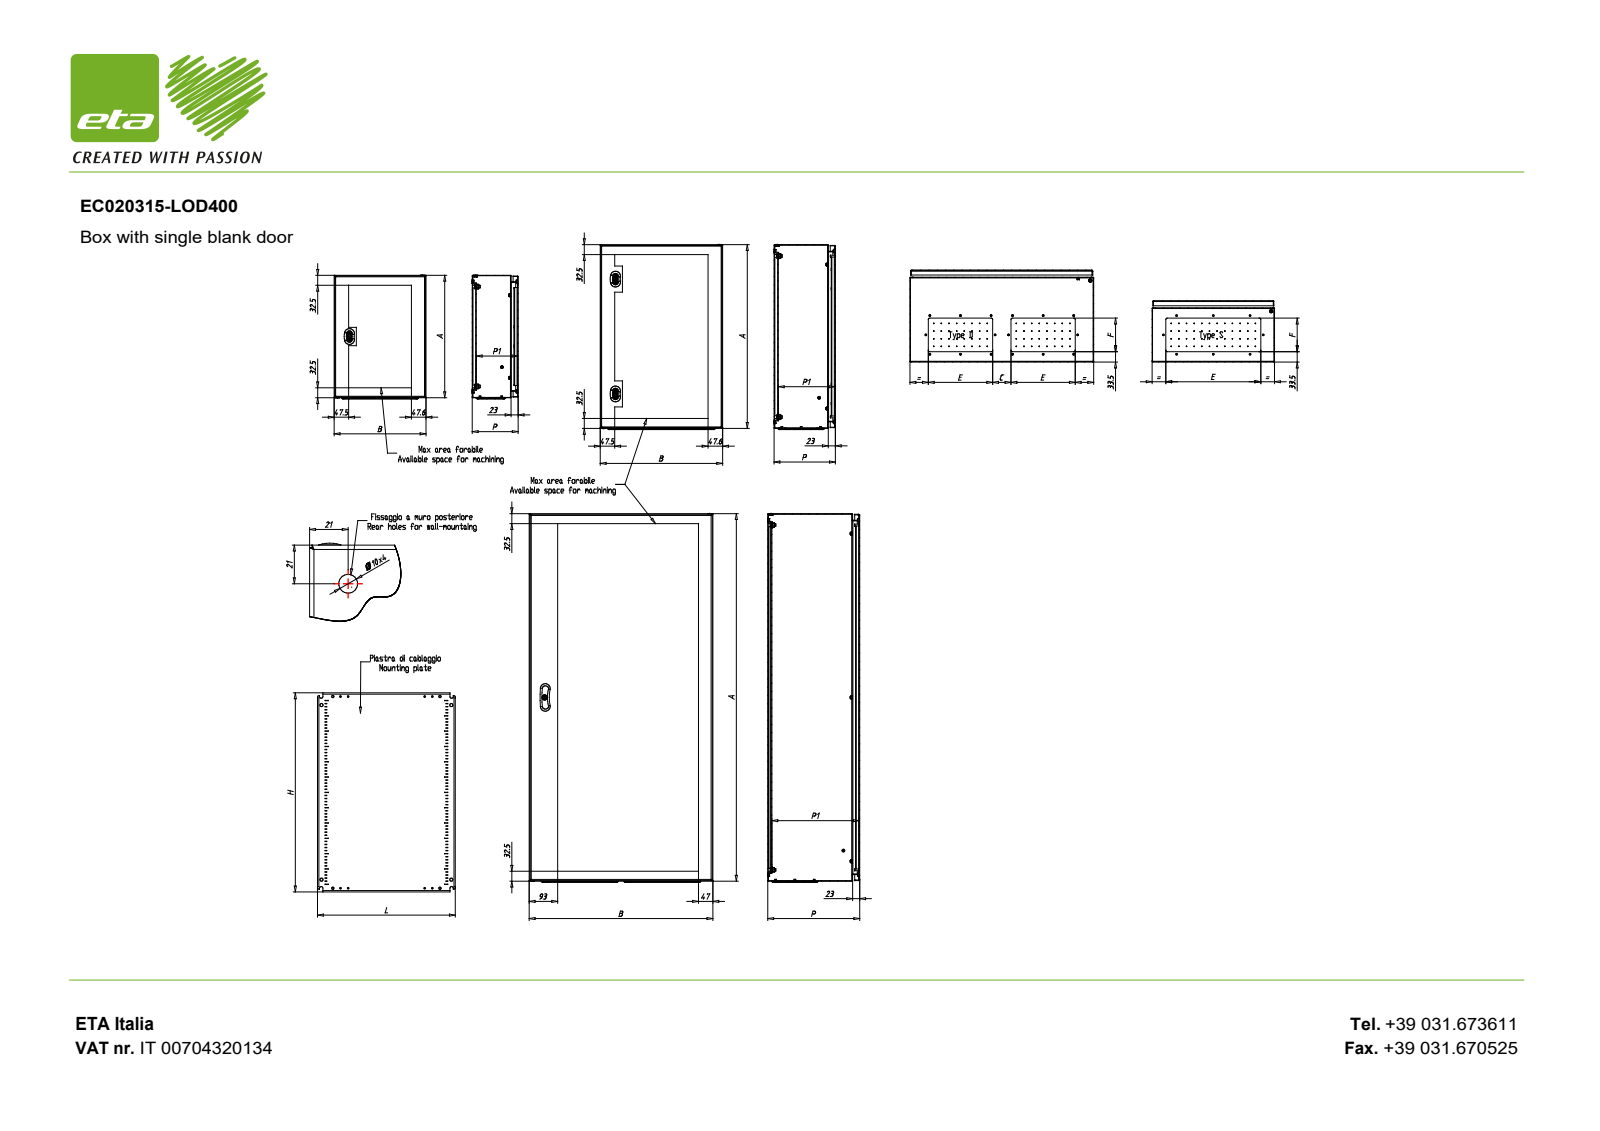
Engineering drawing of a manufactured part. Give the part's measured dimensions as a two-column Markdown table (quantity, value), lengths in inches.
| quantity | value |
| --- | --- |
| part name | EC020315-LOD400; EC020315-LOD400_cabinet; EC020315-LOD400_door; EC020315-LOD400_bottom_plate (+1 more) |
| STEP written by | PARTsolutions (AUTOMOTIVE_DESIGN) |
| units | inches |
| bodies | 4 solids, 362 faces (156 planar, 136 cylindrical, 70 other) |
| overall size | 11.969 × 7.874 × 6.102 |
| volume | 31.96 in³ |
| surface area | 1 105 in² |
| round holes (diameter × count) | 0.177 × 12, 0.039 × 10, 0.394 × 10, 0.197 × 4, 0.217 × 4 |
| round bosses / shafts (diameter × count) | 0.315 × 7, 0.551 × 4, 0.236 × 3 |
| partial cylindrical surfaces (radius × count) | 0.098 × 24, 0.039 × 12, 0.197 × 12, 0.059 × 8, 0.012 × 4, 0.217 × 4, 0.846 × 4, 0.433 × 1 |
| main face-to-face distances | 0.047, 0.059, 7.827, 5.858, 5.906, 5.799, 5.846, 0.157, 5.327, 0.472 |
| hole center spacings | 0.984, 1.969, 4.921, 1.392, 5.019, 2.201, 5.906, 7.687 |
